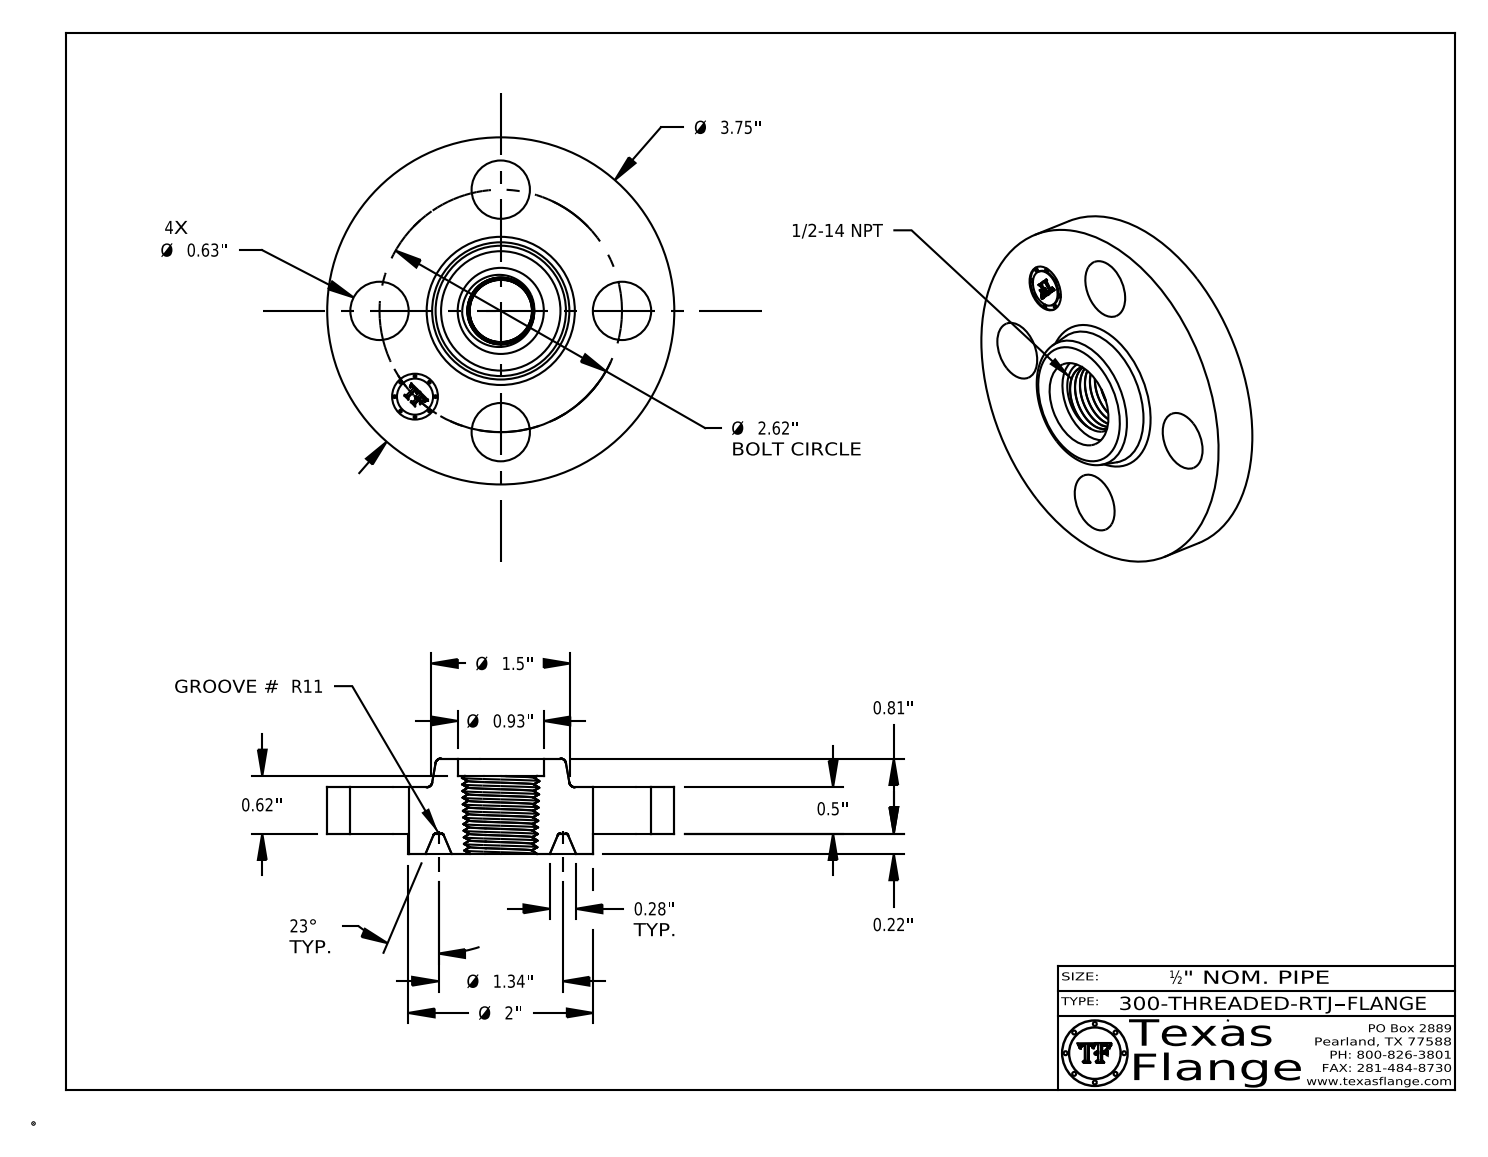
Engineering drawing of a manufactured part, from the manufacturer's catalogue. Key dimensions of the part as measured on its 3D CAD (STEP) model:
Part name (STEP PRODUCT): 300-THREADED-RTJ
STEP written by: CATIA V5 STEP AP214 (AUTOMOTIVE_DESIGN)
Units: inches
Bodies: 1 solid, 547 faces (372 planar, 38 cylindrical, 137 other)
Overall size (bounding box): 3.75 × 3.75 × 1.029
Volume: 5.418 in³ · Surface area: 36.49 in²
Round holes (diameter × count): ⌀0.63 ×4, ⌀0.495 ×1, ⌀0.93 ×1
Round bosses / shafts (diameter × count): ⌀0.03 ×8, ⌀3.75 ×1, ⌀2 ×1, ⌀0.39 ×1
Main face-to-face distances: 0.5, 0.219, 0.719, 1.029, 0.81, 0.31, 0.839, 0.62, 0.12, 0.19
Hole centre spacings: 1.31, 1.852, 1.003, 2.42, 2.62, 1.31
